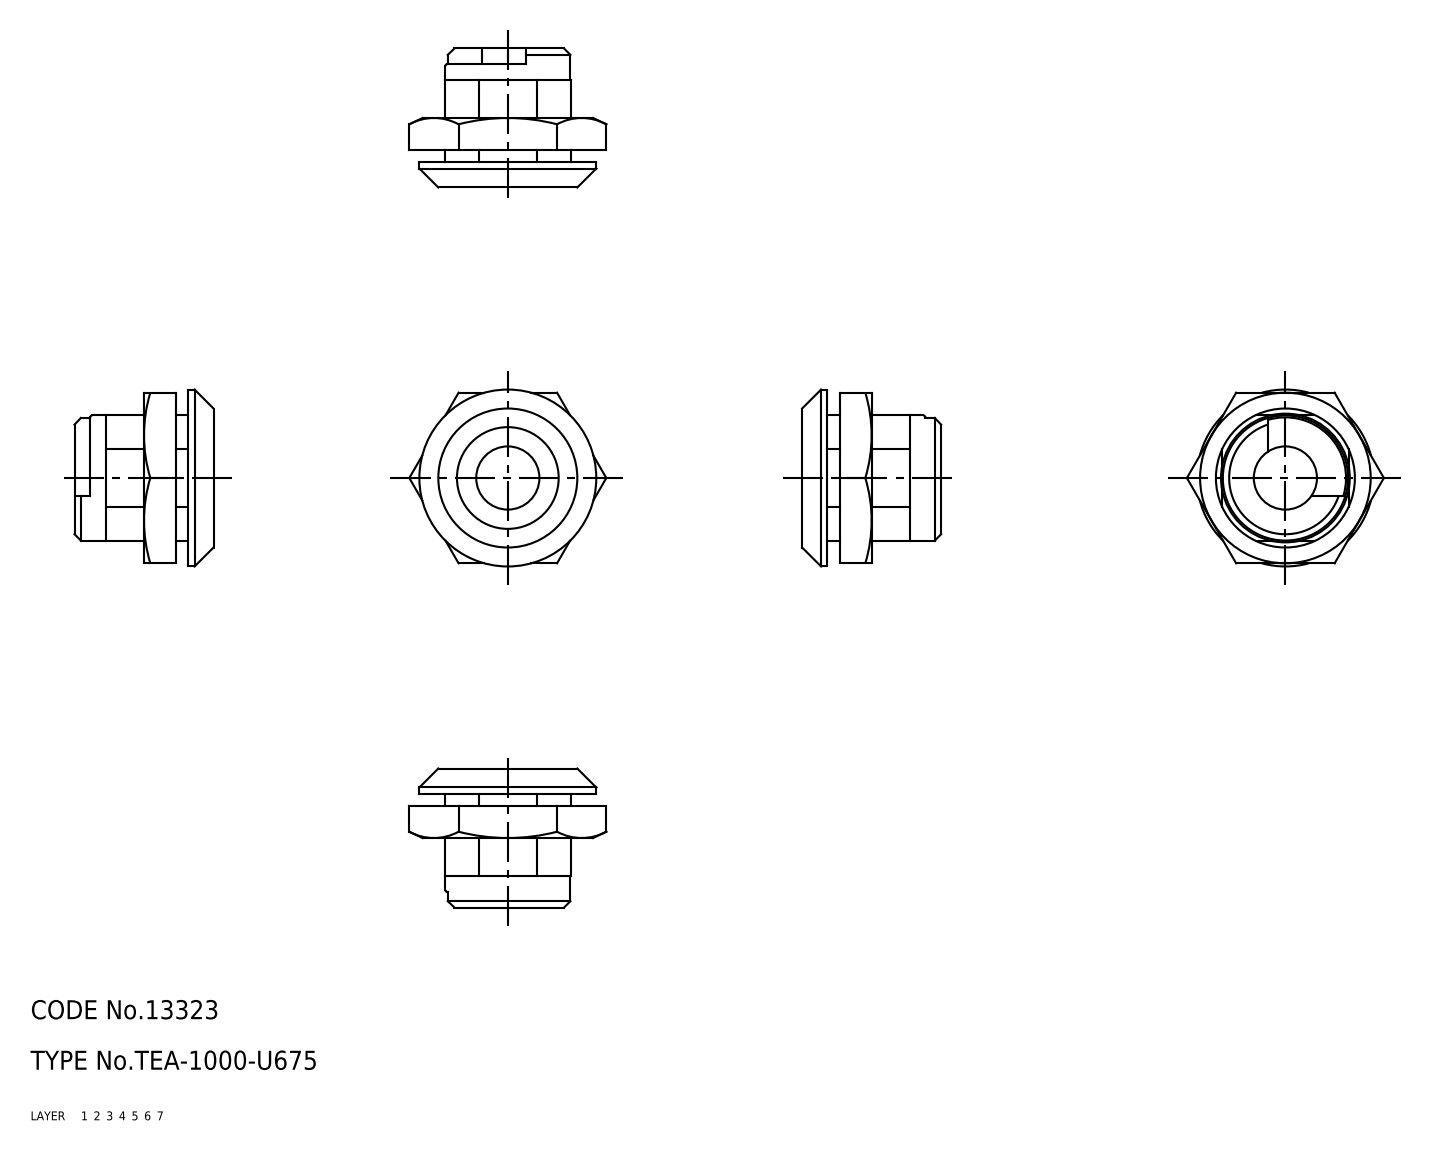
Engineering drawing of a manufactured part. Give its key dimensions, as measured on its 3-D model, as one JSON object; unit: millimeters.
{"part_name": "nut; housing; TEA_1000_U675_12007_36", "step_written_by": "CADfix (AUTOMOTIVE_DESIGN)", "units": "millimeters", "bodies": {"solids": 2, "faces": 48, "planar": 0, "cylindrical": 0, "other": 48}, "overall_size": [31.18, 28, 22], "volume_mm3": 5577, "surface_area_mm2": 4616}
